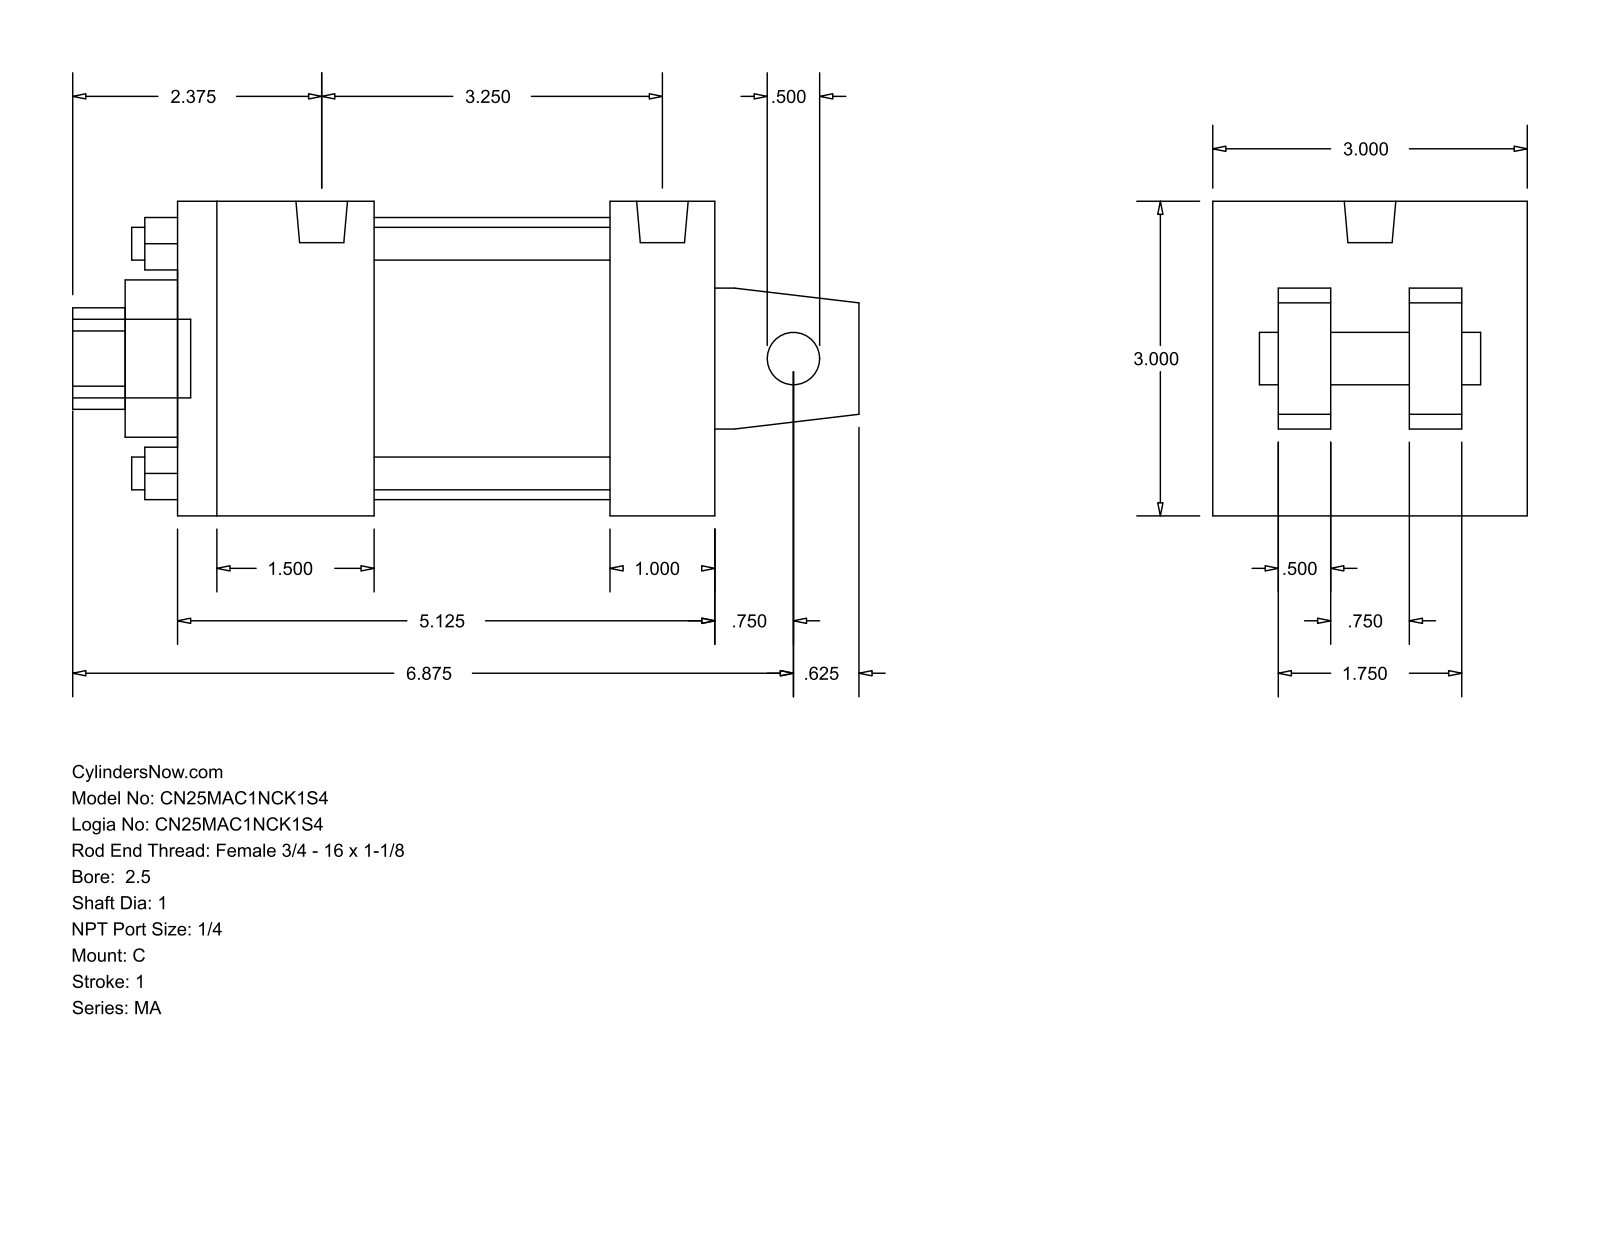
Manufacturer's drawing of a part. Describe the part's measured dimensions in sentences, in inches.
The part is named "MA_C__0250_1". Its 3-D file was written by "GSSL Pune (CONFIG_CONTROL_DESIGN)". It is 0 solids with 103 faces: 76 planar, 27 cylindrical and 0 other. Overall it measures 7.5 by 3 by 3 inches. Round holes: 4 of diameter 0.313, 1 of diameter 0.5, 1 of diameter 1, 1 of diameter 1.5, 1 of diameter 2.69. Round bosses or shafts: 4 of diameter 0.313, 2 of diameter 0.492, 1 of diameter 0.75. Partial cylindrical surfaces (rounded edges, fillets, slot ends): 1 of radius 0.484. The main face-to-face distances are 3, 1.875, 5.125, 0.5, 0.625, 2.375, 1.125, 4.125, 2.25, 3.25. The hole center spacings are 1.548, 2.19, 3.097.
